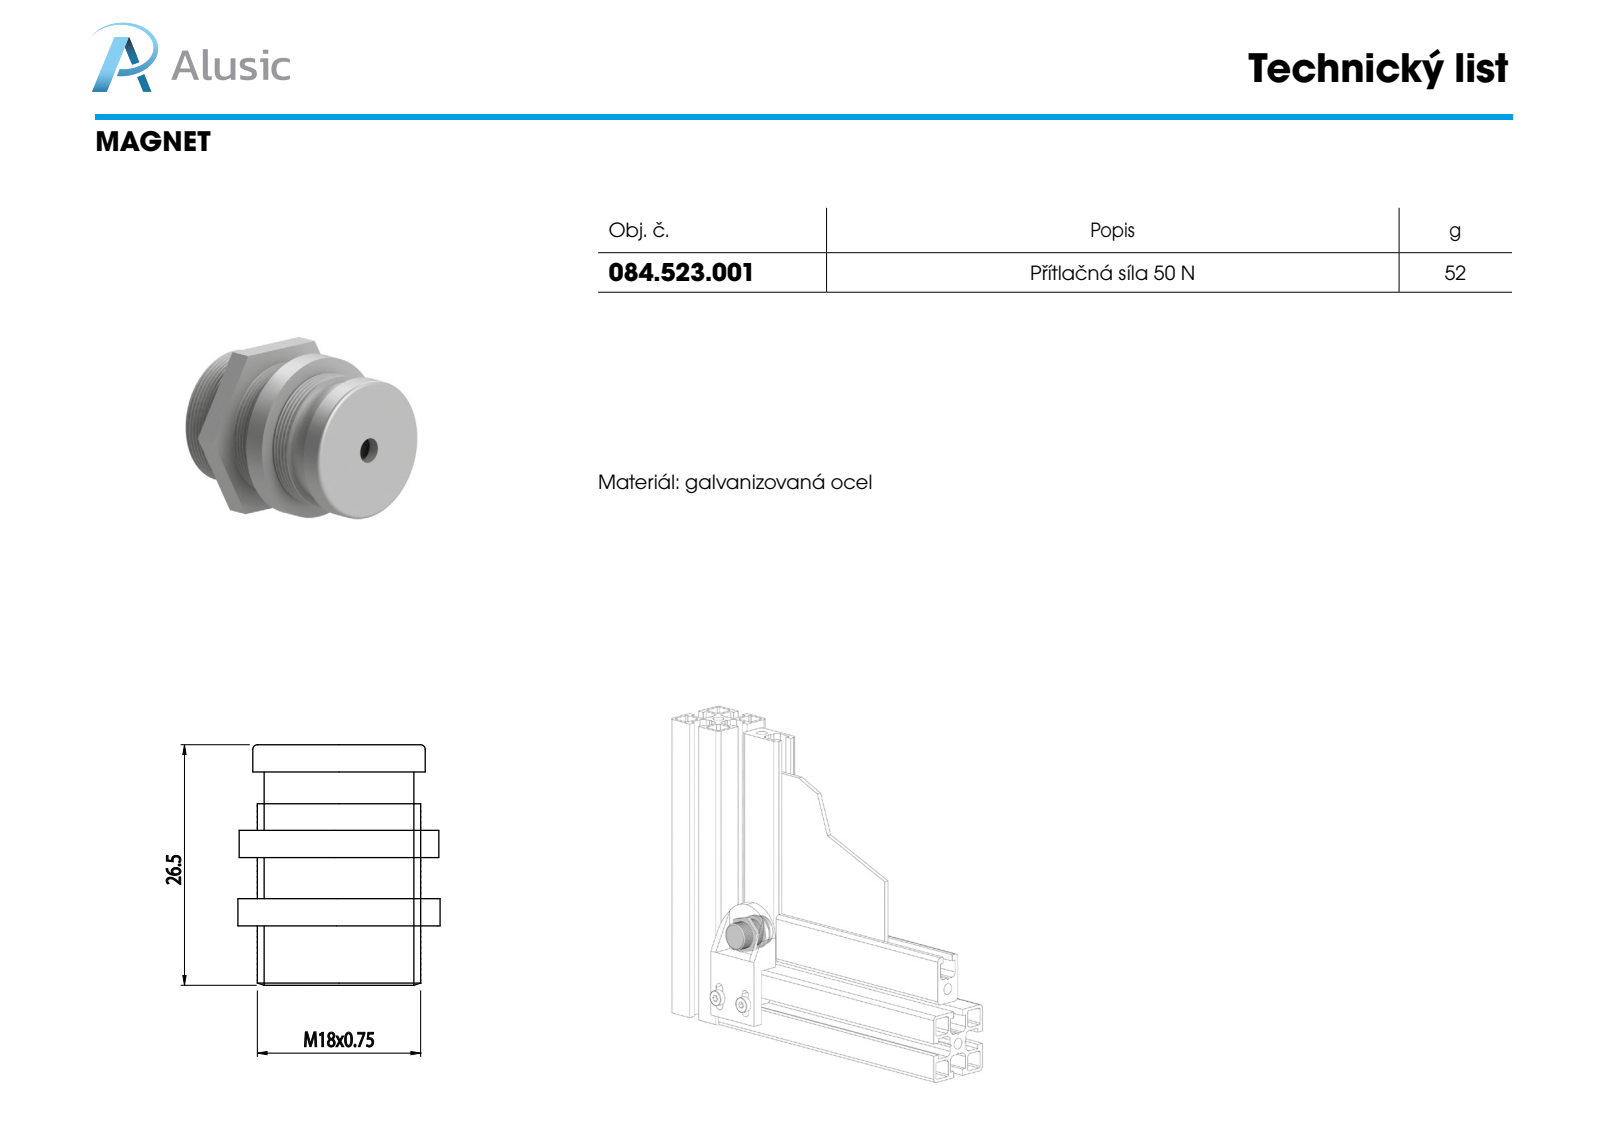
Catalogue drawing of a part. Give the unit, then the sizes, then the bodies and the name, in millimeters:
Units: millimetres
Overall size (bounding box): 26.5 × 19 × 19
Round holes (diameter × count): ⌀3.4 ×1
Round bosses / shafts (diameter × count): ⌀19 ×1, ⌀18 ×1, ⌀16.5 ×1
Partial cylindrical surfaces — rounded edges, fillets, slot ends (radius × count): R7.75 ×1
Main face-to-face distances: 3, 23.5, 26.5, 4, 22.5, 1, 20, 2.5, 3.5, 6.5
Volume: 6 235 mm³ · Surface area: 4 417 mm²
Bodies: 2 solids, 219 faces (8 planar, 75 cylindrical, 136 other)
Part name (STEP PRODUCT): 084.523.001
STEP written by: SolidWorks 2011 (CONFIG_CONTROL_DESIGN)
